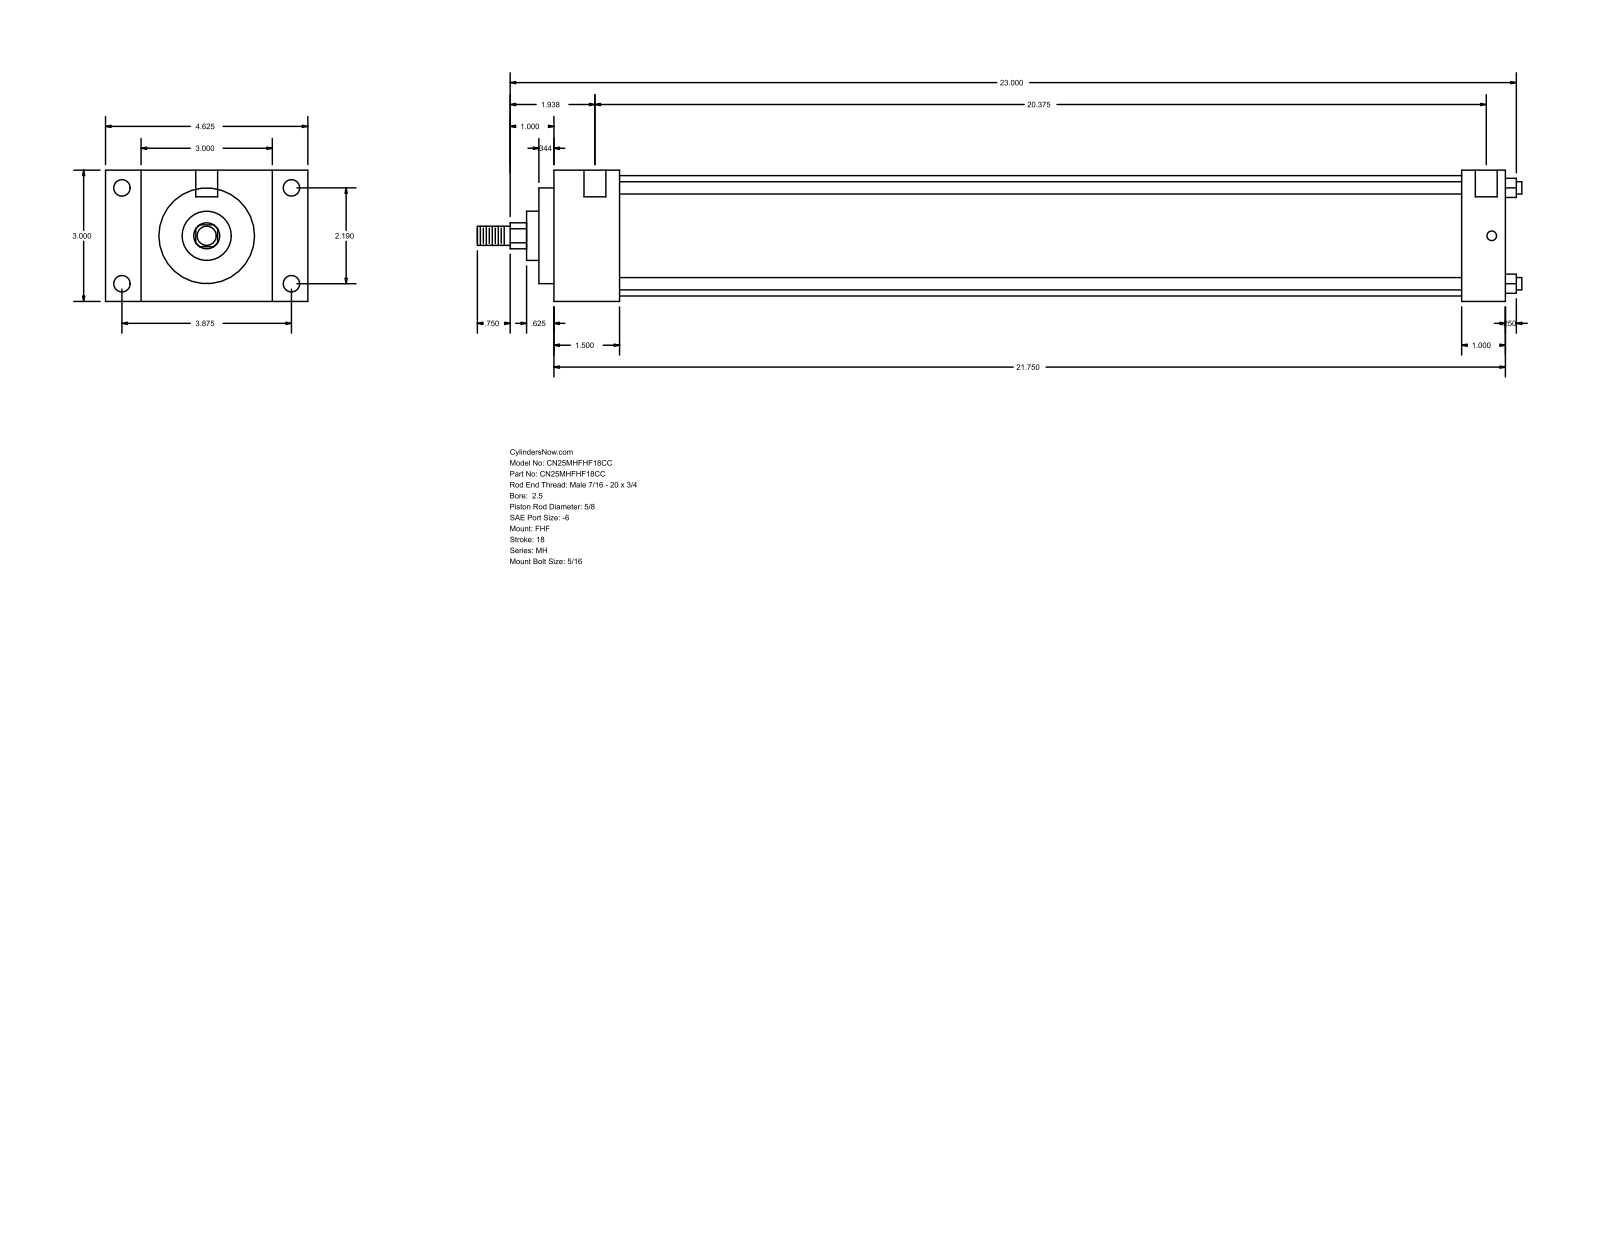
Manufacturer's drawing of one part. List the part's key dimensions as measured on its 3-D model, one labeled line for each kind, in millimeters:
Part name (STEP PRODUCT): MH_FHF__0250_0.625
STEP written by: GSSL Pune (CONFIG_CONTROL_DESIGN)
Units: millimetres
Bodies: 0 solids, 90 faces (61 planar, 29 cylindrical, 0 other)
Overall size (bounding box): 606.42 × 117.47 × 76.2
Round holes (diameter × count): ⌀5.56 ×4, ⌀9.53 ×4, ⌀12.7 ×2
Round bosses / shafts (diameter × count): ⌀7.14 ×4, ⌀69.85 ×1, ⌀55.55 ×1, ⌀28.57 ×1, ⌀15.88 ×1, ⌀11.11 ×1
Partial cylindrical surfaces — rounded edges, fillets, slot ends (radius × count): R7.54 ×1
Main face-to-face distances: 76.2, 552.45, 38.1, 514.35, 20.64, 96.84, 117.48, 25.4, 527.05, 488.95
Hole centre spacings: 55.62, 98.42, 113.05, 525.46, 3.17, 4.76, 517.53, 520.7
